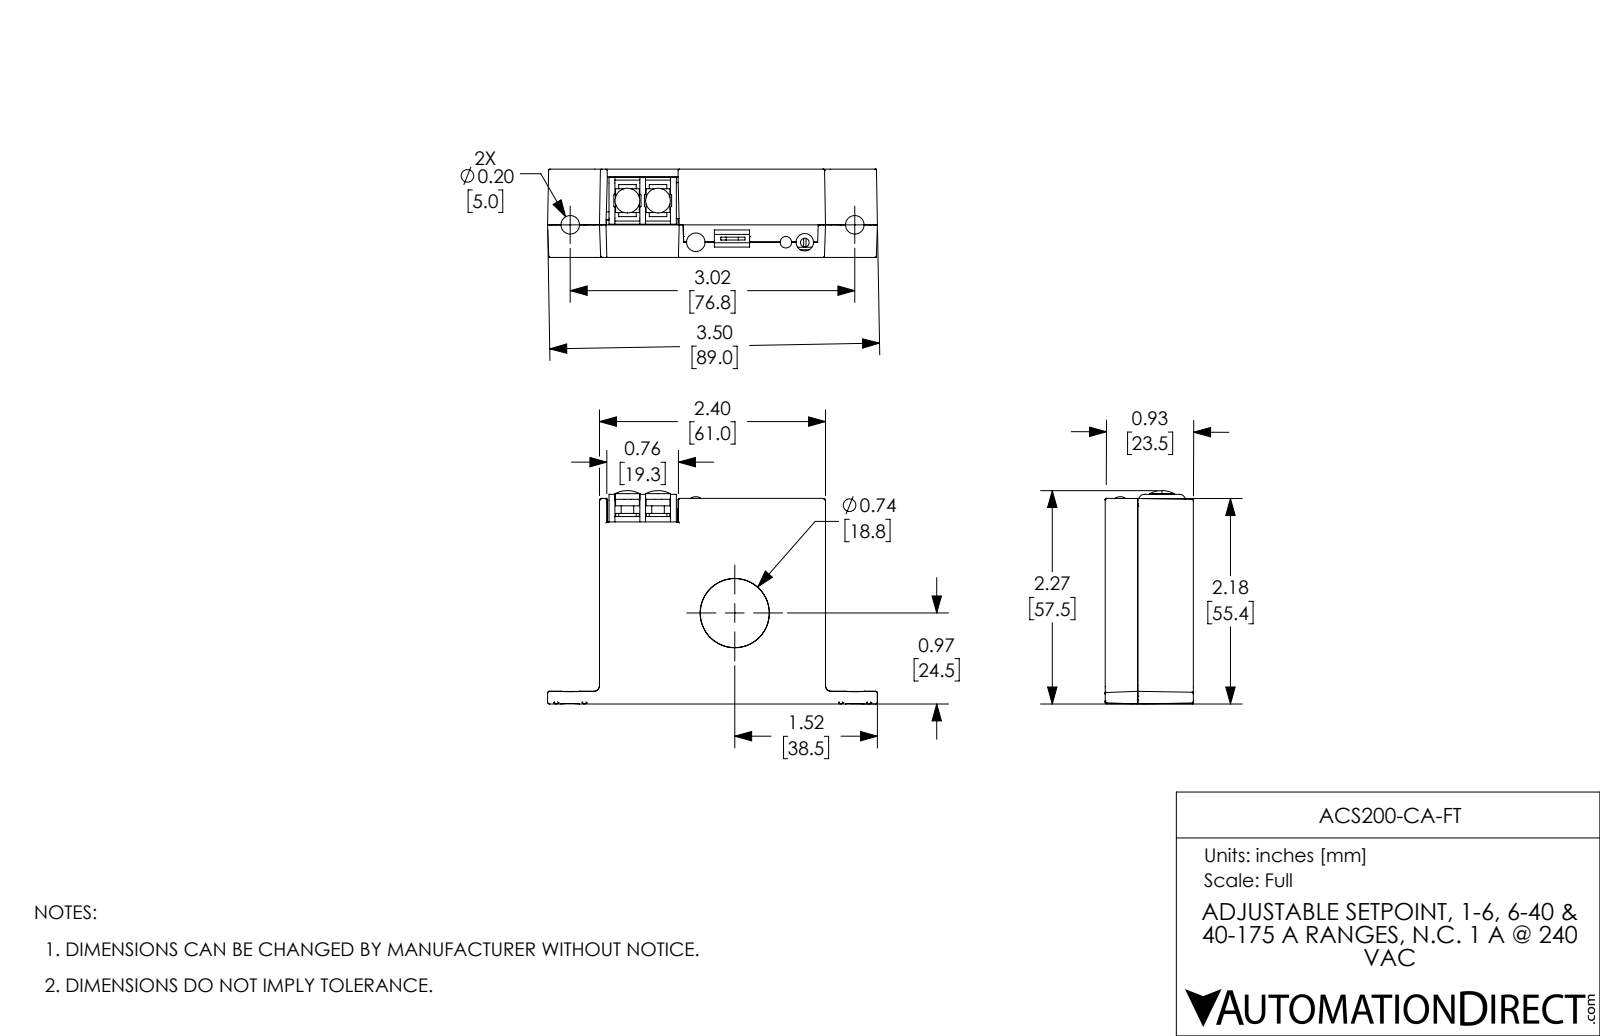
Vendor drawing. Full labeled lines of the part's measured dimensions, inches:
Part name (STEP PRODUCT): ACS200-CA-FT
STEP written by: SolidWorks 2017 (AUTOMOTIVE_DESIGN)
Units: inches
Bodies: 8 solids, 550 faces (360 planar, 126 cylindrical, 64 other)
Overall size (bounding box): 3.504 × 2.265 × 0.937
Volume: 1.893 in³ · Surface area: 53.16 in²
Round holes (diameter × count): ⌀0.045 ×4, ⌀0.197 ×3, ⌀0.147 ×2, ⌀0.122 ×1, ⌀0.185 ×1, ⌀0.82 ×1
Round bosses / shafts (diameter × count): ⌀0.043 ×4, ⌀0.263 ×2, ⌀0.134 ×2, ⌀0.807 ×1, ⌀0.234 ×1, ⌀0.194 ×1, ⌀0.093 ×1
Partial cylindrical surfaces — rounded edges, fillets, slot ends (radius × count): R0.012 ×20, R0.02 ×12, R0.03 ×8, R0.059 ×4, R0.008 ×2, R0.063 ×2
Main face-to-face distances: 0.083, 0.854, 0.937, 0.772, 0.442, 0.349, 0.413, 0.266, 0.33, 0.064
Hole centre spacings: 2.151, 3.535, 0.201, 0.325, 0.563, 0.598, 0.66, 0.755
